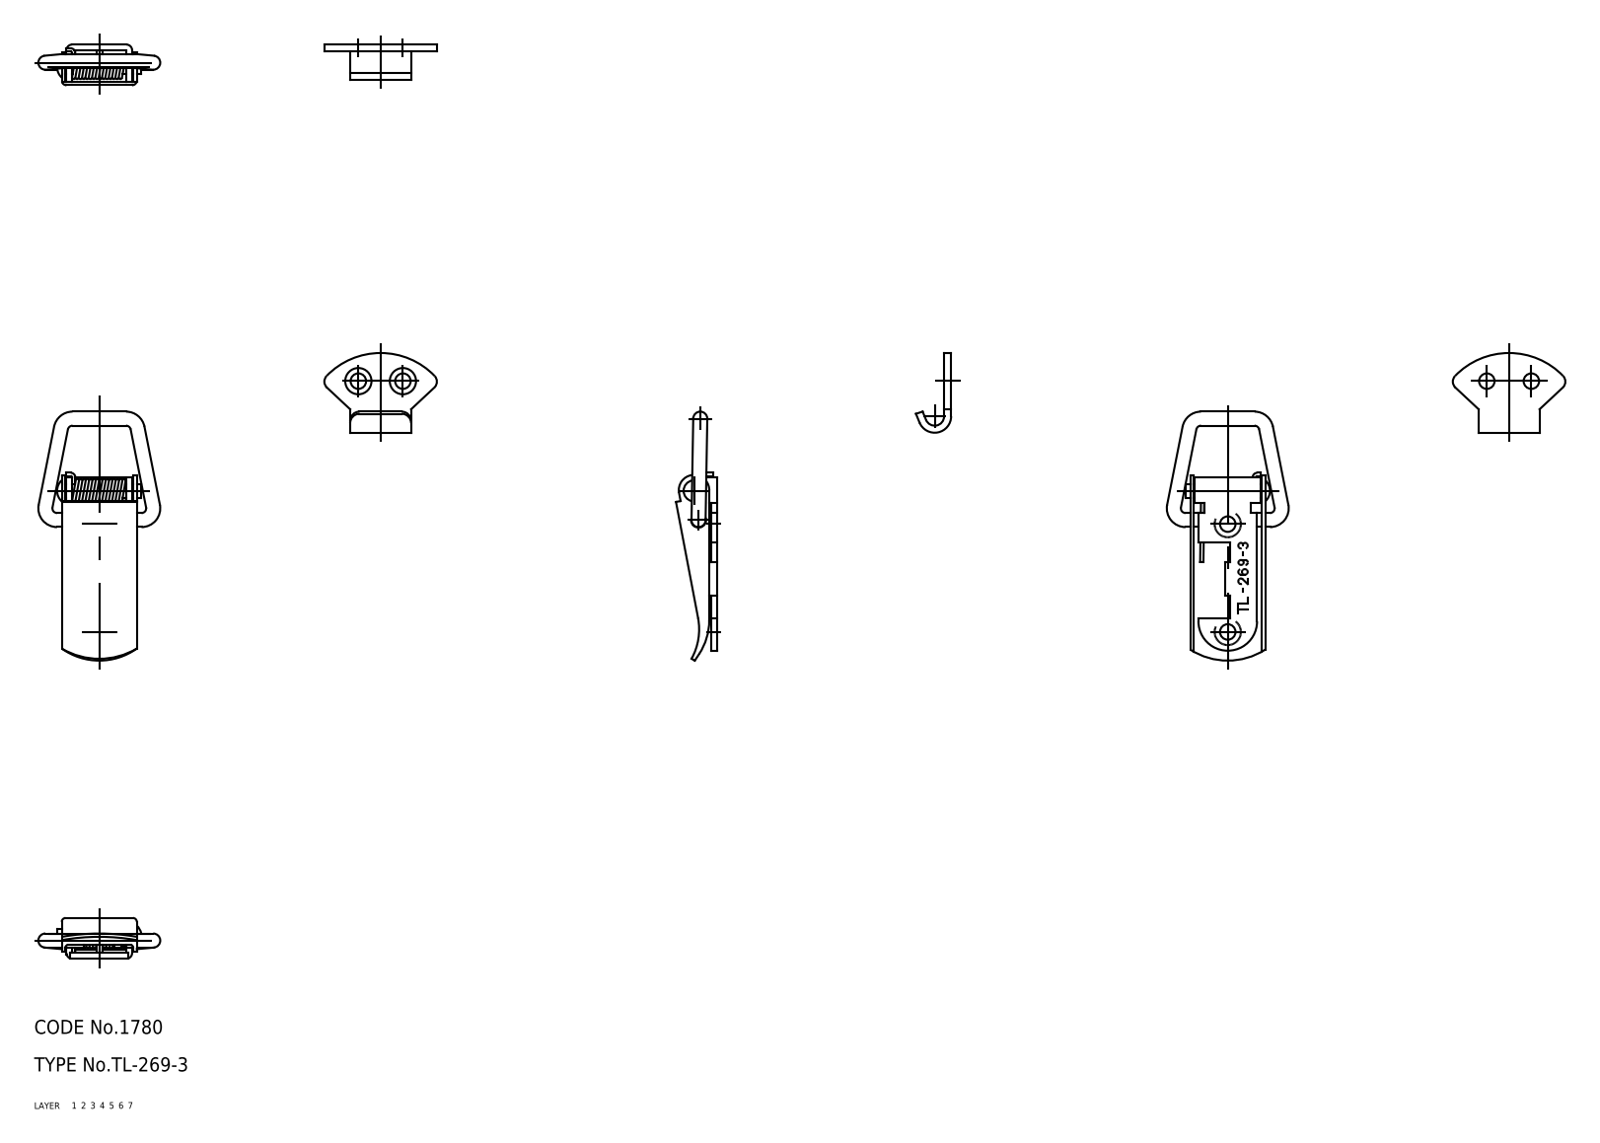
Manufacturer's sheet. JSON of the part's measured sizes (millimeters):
{"part_name": "67129232; 67129245; 67129258; 67129271 (+7 more)", "step_written_by": "CADfix (AUTOMOTIVE_DESIGN)", "units": "millimeters", "bodies": {"solids": 5, "faces": 150, "planar": 0, "cylindrical": 0, "other": 150}, "overall_size": [65.61, 26, 8.68], "volume_mm3": 2233, "surface_area_mm2": 4730}
